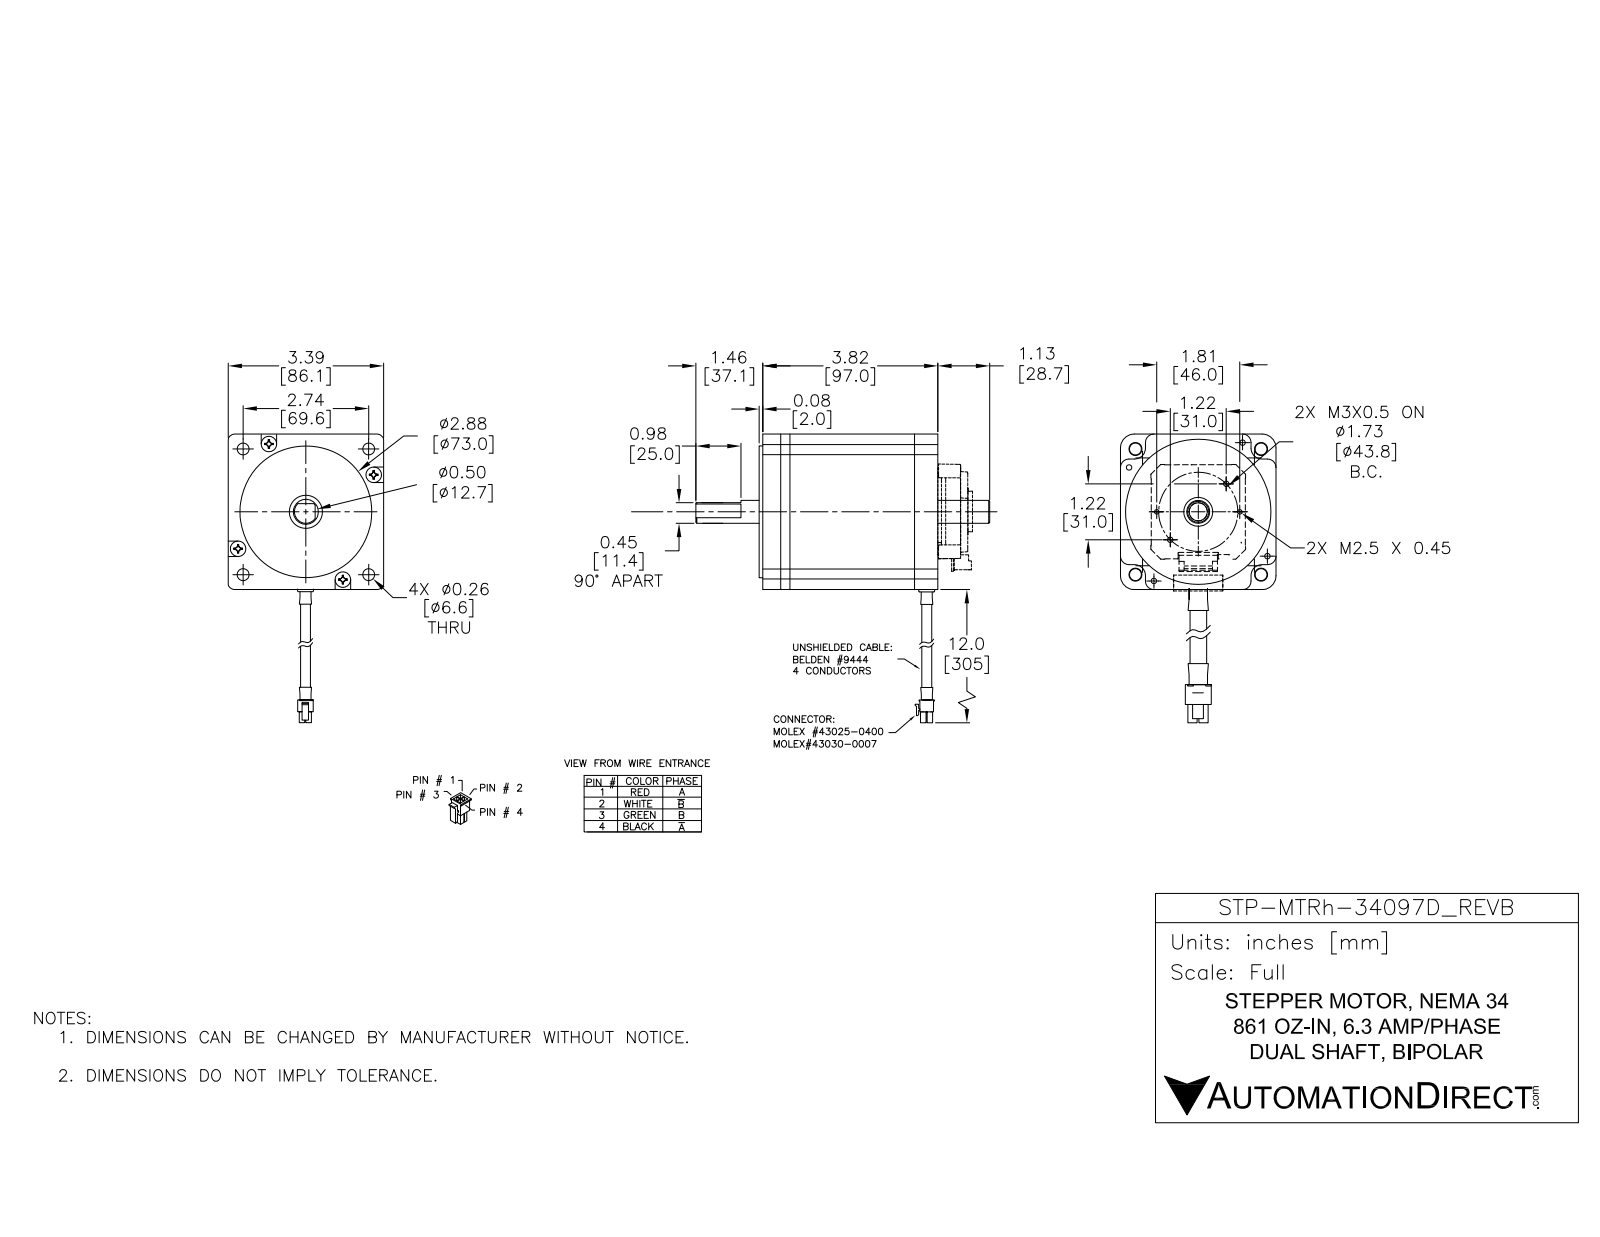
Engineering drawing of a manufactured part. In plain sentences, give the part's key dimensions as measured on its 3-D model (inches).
The part is named "8718M-16PD-33RO Coord fXT". Its 3-D file was written by "SolidWorks 2017 (AUTOMOTIVE_DESIGN)". It is 1 solid with 205 faces: 107 planar, 71 cylindrical and 27 other. Overall it measures 6.39 by 4.386 by 3.39 inches. Its volume is 40.22 cubic inches and its surface area 80.56 square inches. Round holes: 6 of diameter 0.118, 4 of diameter 0.26, 2 of diameter 0.098, 1 of diameter 0.63, 1 of diameter 1.89, 1 of diameter 3.169. Round bosses or shafts: 4 of diameter 0.213, 1 of diameter 2.875, 1 of diameter 1.339, 1 of diameter 0.5, 1 of diameter 0.276. Partial cylindrical surfaces (rounded edges, fillets, slot ends): 8 of radius 0.185, 4 of radius 0.167, 4 of radius 0.236, 4 of radius 0.299. The main face-to-face distances are 3.39, 3.874, 3.795, 0.079, 0.543, 2.846, 3.799, 3.878, 2.303, 3.74. The hole center spacings are 0.426, 1.446, 1.791, 1.937, 2.121, 2.341, 2.533, 2.657.
